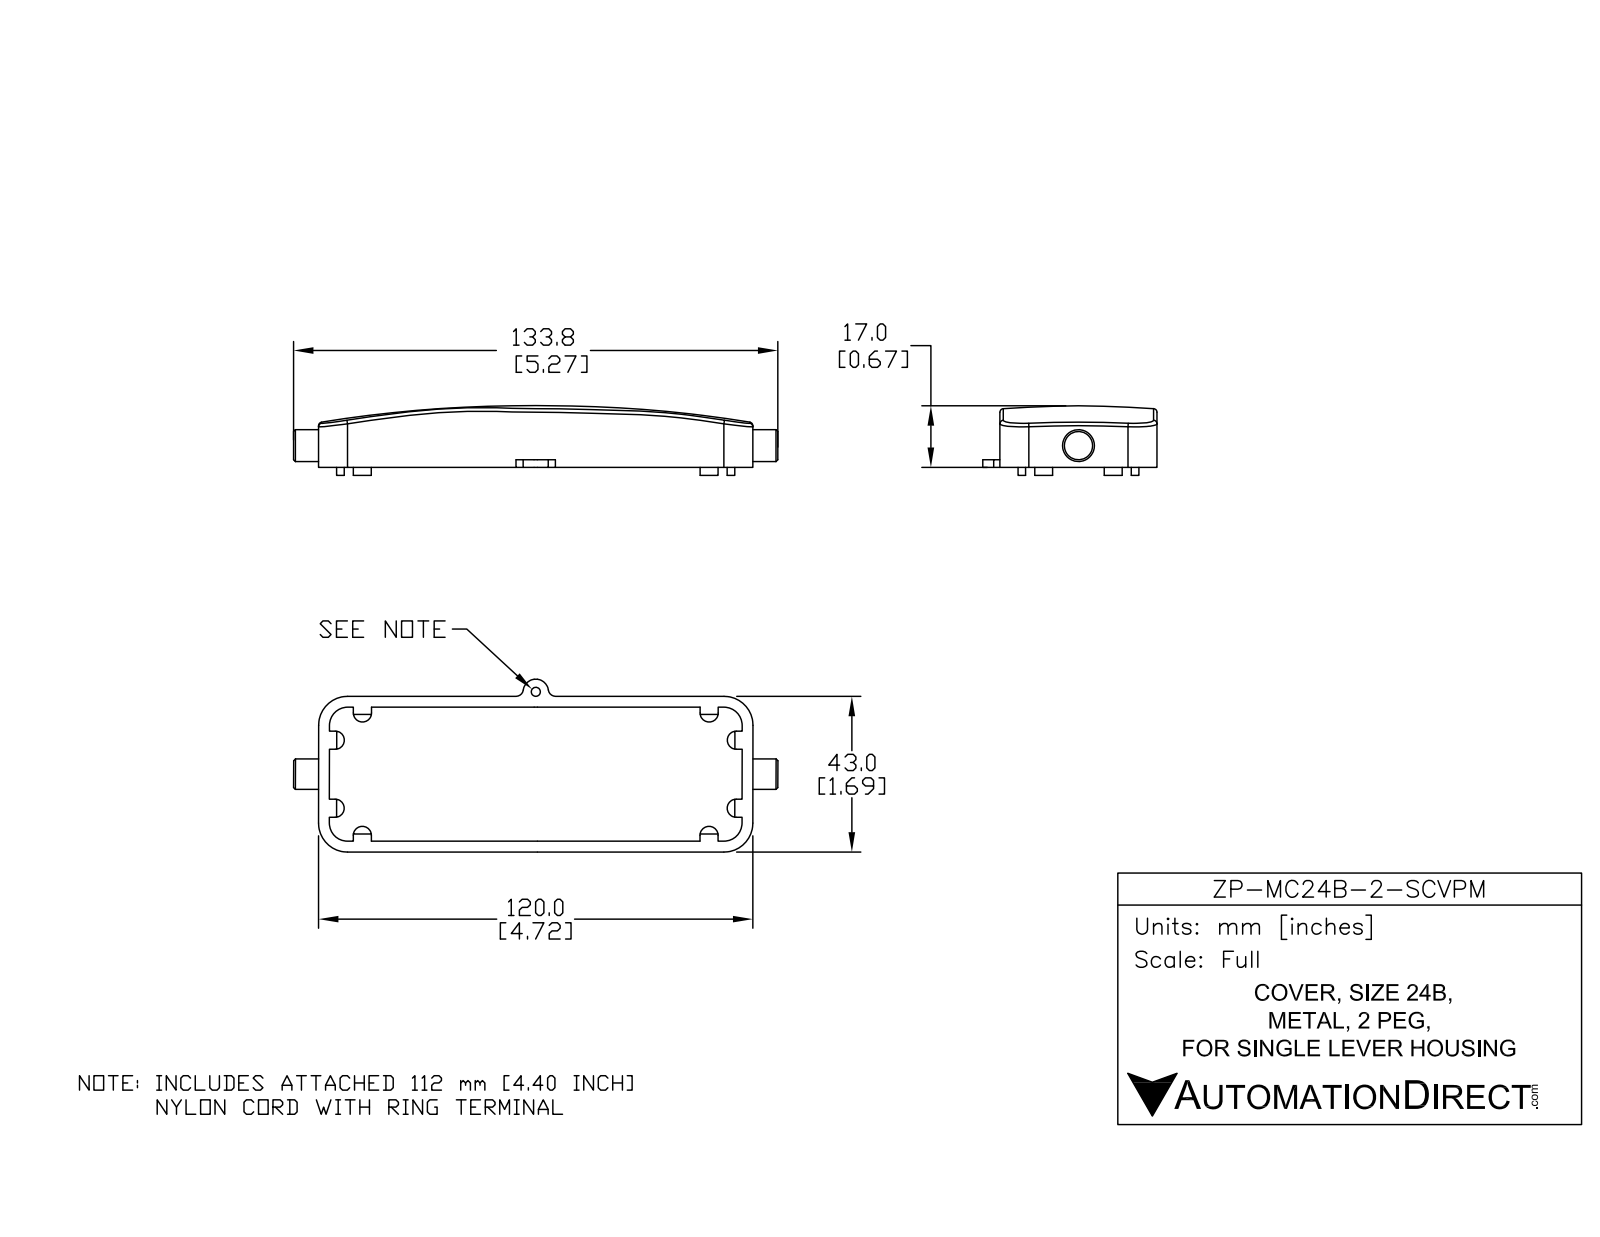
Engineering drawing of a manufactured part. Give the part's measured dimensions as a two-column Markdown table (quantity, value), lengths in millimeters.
| quantity | value |
| --- | --- |
| part name | ZP-MC24B-2-SCVPM |
| STEP written by | SolidWorks 2014 (AUTOMOTIVE_DESIGN) |
| units | millimeters |
| bodies | 4 solids, 129 faces (71 planar, 38 cylindrical, 20 other) |
| overall size | 146.44 × 133.78 × 68.1 |
| volume | 29 993 mm³ |
| surface area | 21 214 mm² |
| round holes (diameter × count) | 2.5 × 1, 4.1 × 1 |
| round bosses / shafts (diameter × count) | 8.8 × 1 |
| partial cylindrical surfaces (radius × count) | 2.5 × 8, 0.45 × 4, 5 × 4, 8 × 4, 0.6 × 2, 2 × 2, 6 × 2, 3.5 × 1 |
| main face-to-face distances | 3, 40.4, 43.4, 37.4, 117, 120, 5, 9.6, 114, 14.6 |
